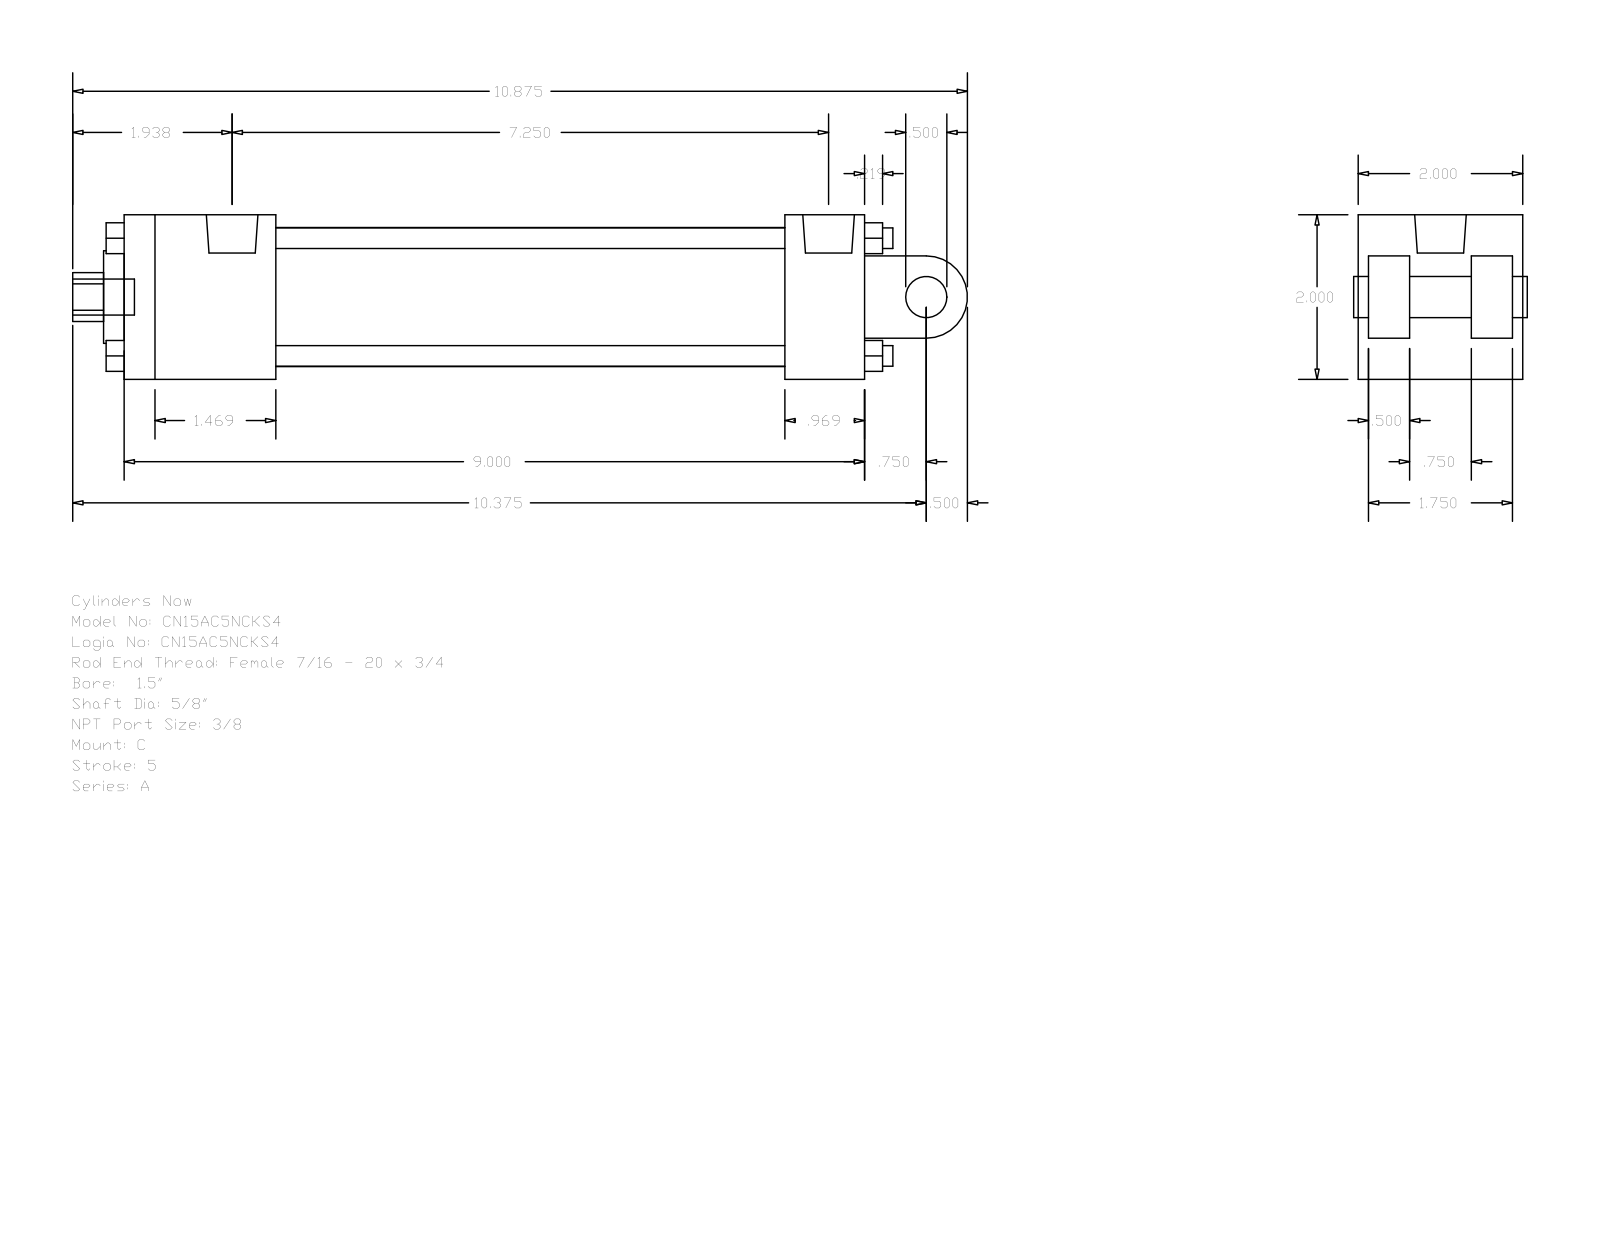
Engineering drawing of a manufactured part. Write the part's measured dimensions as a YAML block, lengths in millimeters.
part_name: "A_C__0150_0.625"
step_written_by: "GSSL Pune (CONFIG_CONTROL_DESIGN)"
units: millimeters
bodies: {solids: 0, faces: 135, planar: 102, cylindrical: 33, other: 0}
overall_size: [276.23, 50.8, 50.8]
round_holes:
  - {diameter: 5.56, count: 2}
  - {diameter: 15.88, count: 1}
  - {diameter: 15.93, count: 1}
  - {diameter: 28.57, count: 1}
  - {diameter: 42.93, count: 1}
round_bosses_or_shafts:
  - {diameter: 6.35, count: 4}
  - {diameter: 5.56, count: 2}
  - {diameter: 15.93, count: 1}
  - {diameter: 12.7, count: 1}
  - {diameter: 11.11, count: 1}
partial_cylinders:
  - {radius: 7.54, count: 1}
  - {radius: 12.7, count: 1}
face_to_face_distances: [50.8, 12.7, 228.59, 3.17, 15.87, 34.93, 47.63, 31.76, 203.99, 24.6]
hole_center_spacings: [3.97]
